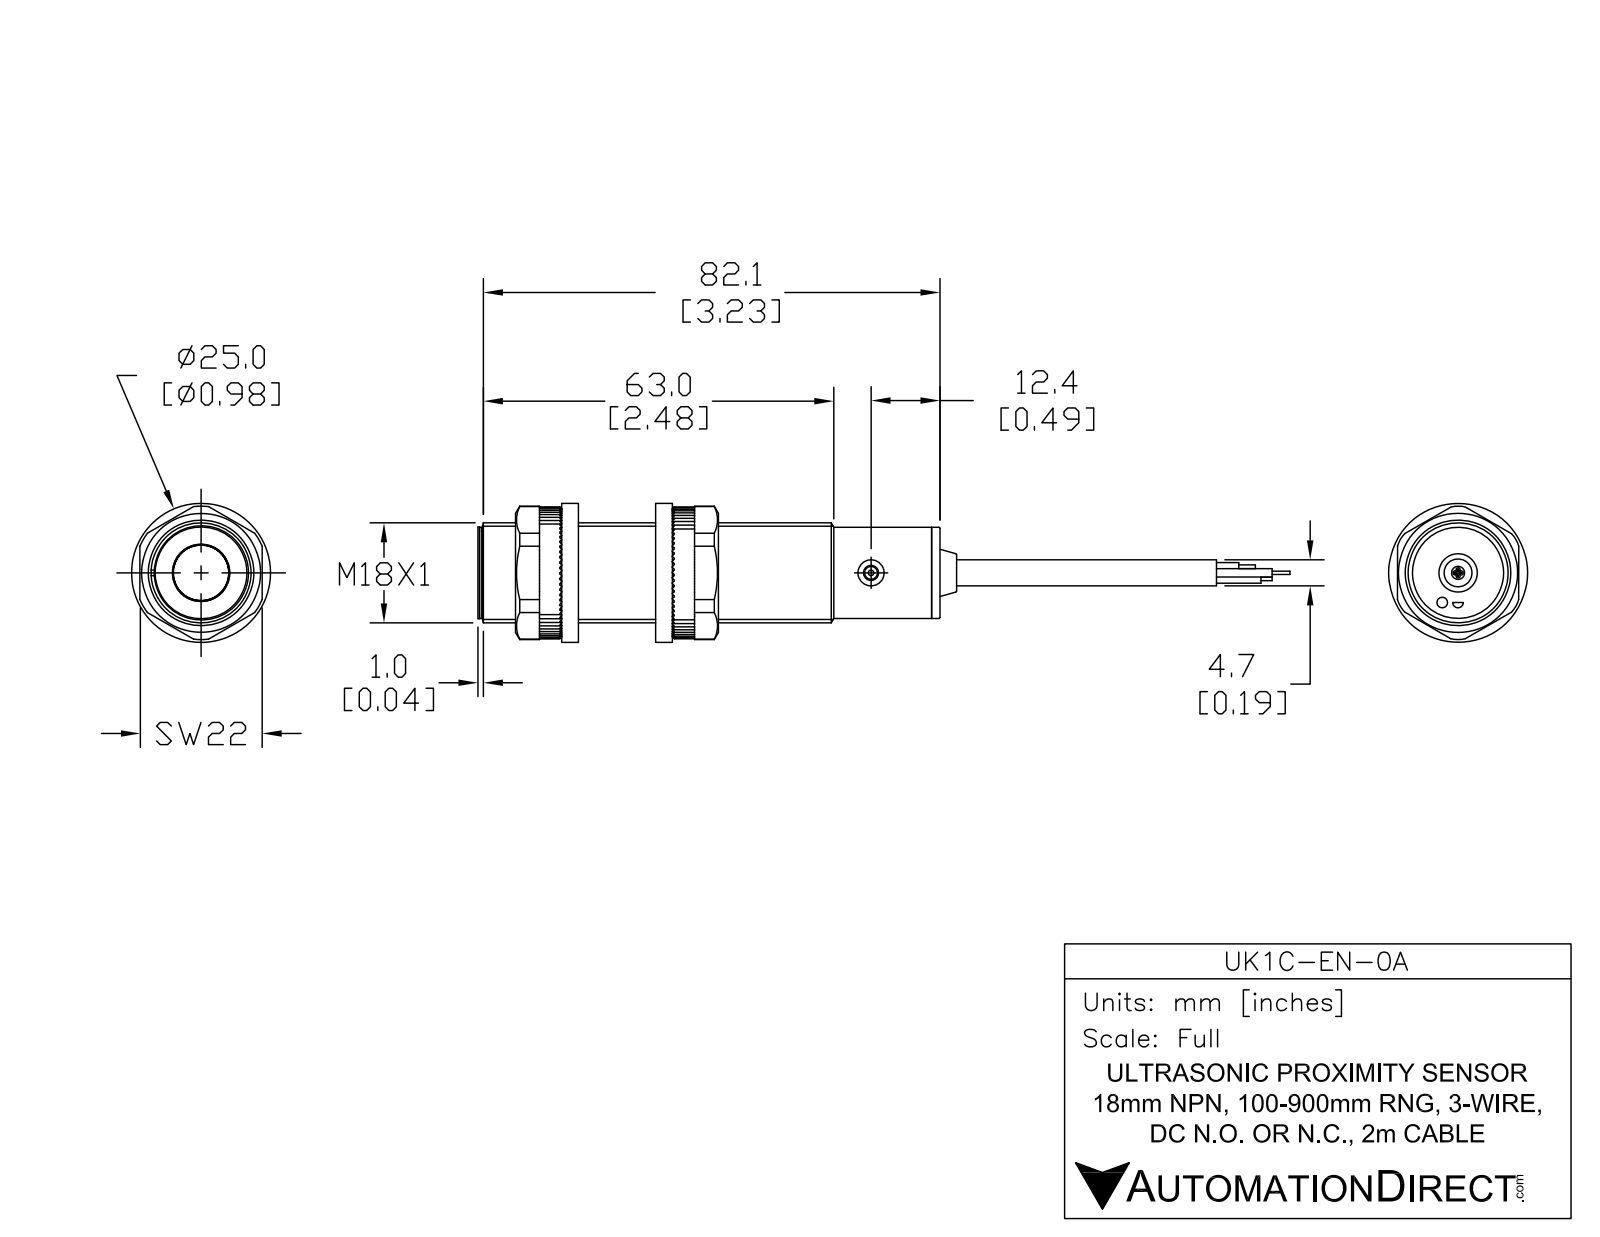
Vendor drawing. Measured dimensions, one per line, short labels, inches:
name: UK1C-EN-0A
written by: SolidWorks 2017 (AUTOMOTIVE_DESIGN)
unit: in
bodies: 6 solids, 55 faces (17 planar, 24 cylindrical, 14 other)
size: 4.832 × 0.709 × 0.709
volume: 1.285 in³; area: 10.69 in²
holes: 2× ⌀0.185, 1× ⌀0.106
bosses: 1× ⌀0.709, 1× ⌀0.646, 1× ⌀0.622, 1× ⌀0.374, 1× ⌀0.189, 1× ⌀0.091
face distances: 3.193, 3.252, 0.059, 0.039, 3.232, 3.291, 0.041, 3.234, 3.293, 3.257
